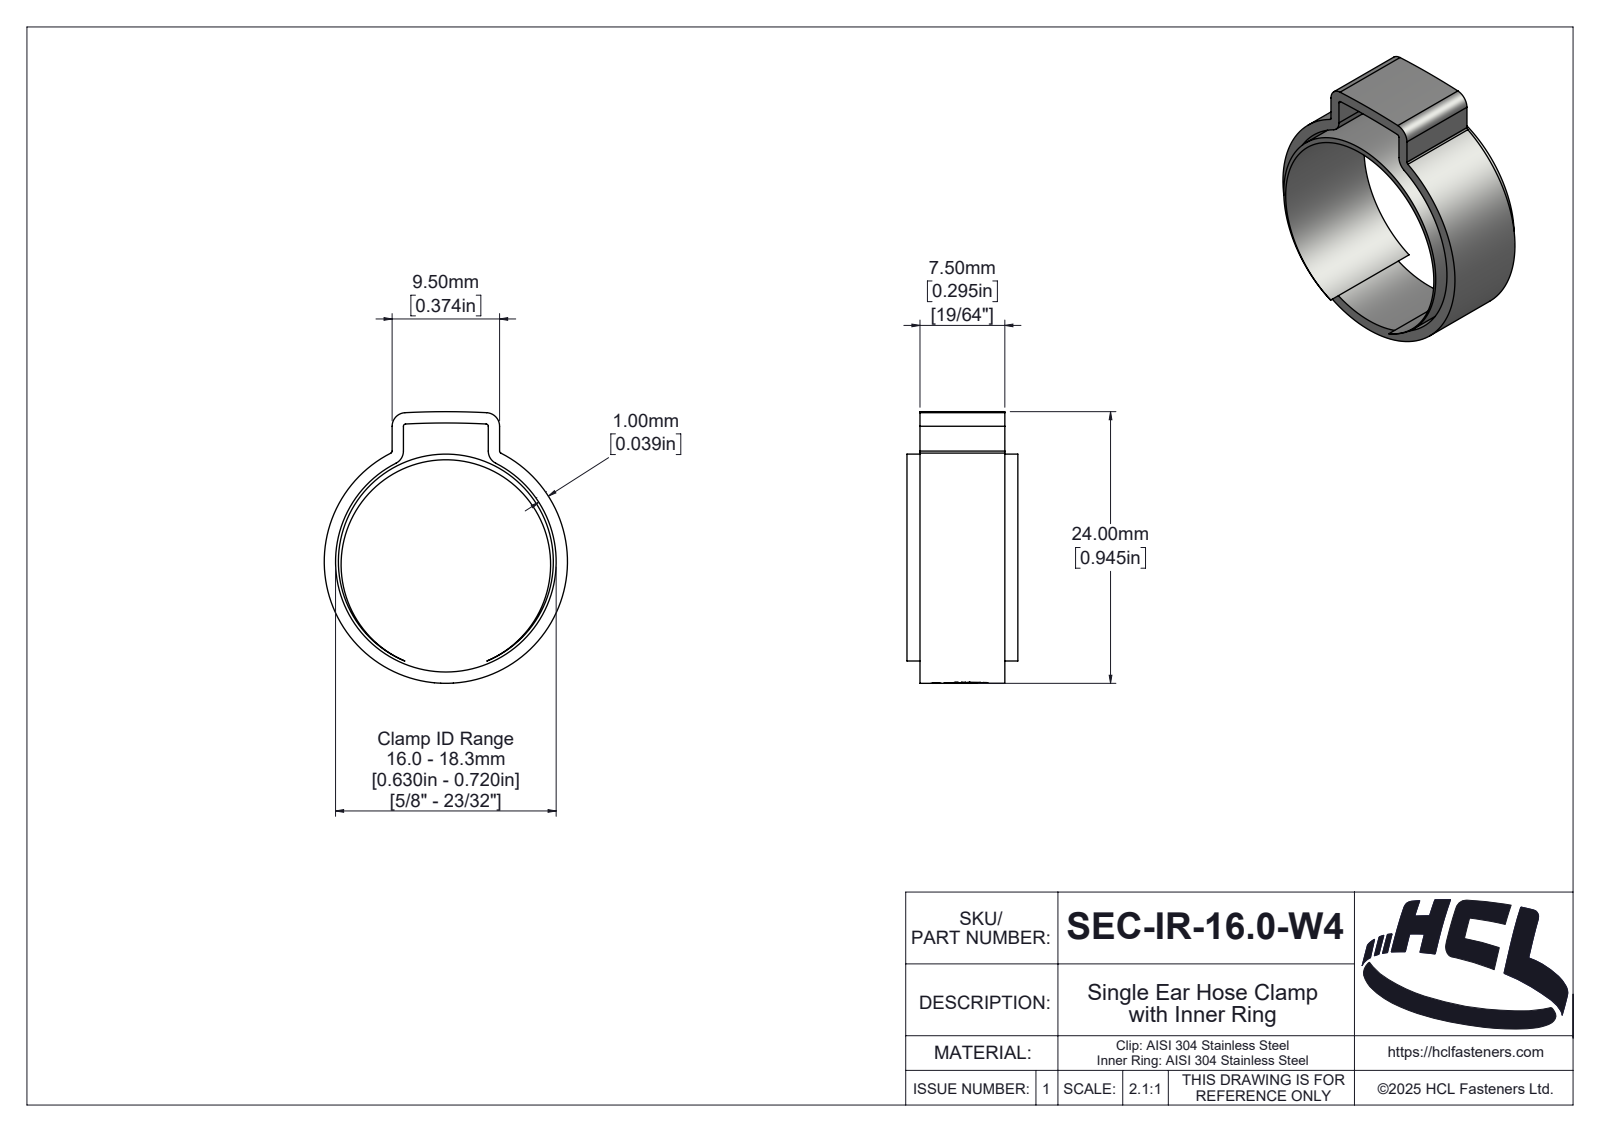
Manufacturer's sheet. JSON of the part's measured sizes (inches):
{"part_name": "SEC-IR-16.0-W4", "step_written_by": "SolidWorks 2025 (AUTOMOTIVE_DESIGN)", "units": "inches", "bodies": {"solids": 2, "faces": 131, "planar": 10, "cylindrical": 72, "other": 49}, "overall_size": [0.945, 0.846, 0.386], "volume_in3": 0.041, "surface_area_in2": 3.46, "round_holes": [[0.729, 1], [0.768, 1]], "round_bosses_or_shafts": [[0.846, 1], [0.748, 1]], "partial_cylinders_radius": [[0.008, 4], [0.047, 4], [0.008, 1], [0.035, 1], [0.043, 1], [0.045, 1], [0.055, 1], [0.078, 1]], "face_to_face_distances": [0.295, 0.039, 0.335, 0.045, 0.341, 0.374, 0.386, 0.176, 0.136, 0.159]}
